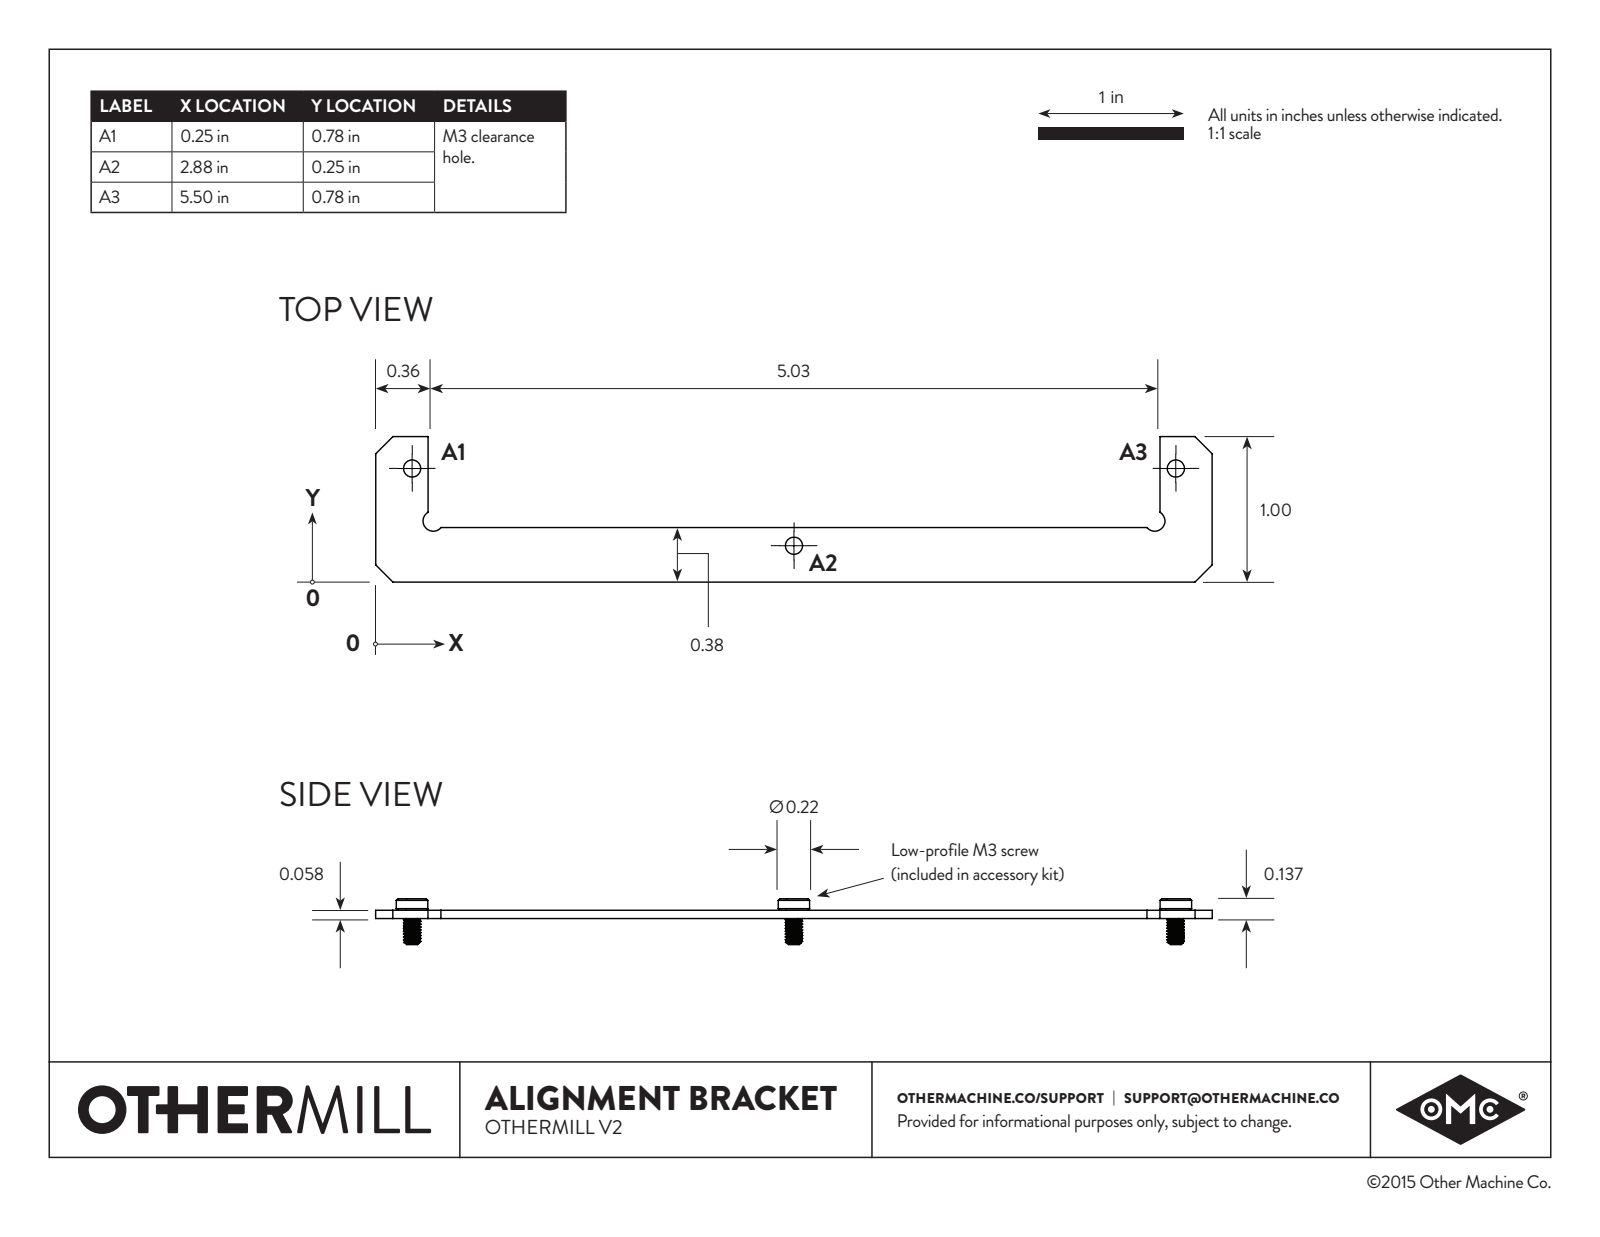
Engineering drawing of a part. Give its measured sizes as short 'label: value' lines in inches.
name: DoubleSidedBracket-V2B
written by: SolidWorks 2015 (CONFIG_CONTROL_DESIGN)
unit: in
bodies: 1 solid, 23 faces (14 planar, 9 cylindrical, 0 other)
size: 5.75 × 1 × 0.04
volume: 0.101 in³; area: 5.701 in²
holes: 3× ⌀0.118
rounds: 2× R0.07
face distances: 0.04, 0.375, 0.359, 5.391, 5.75, 5.031, 1, 0.625, 4.606
hole spacings: 2.678, 5.25
